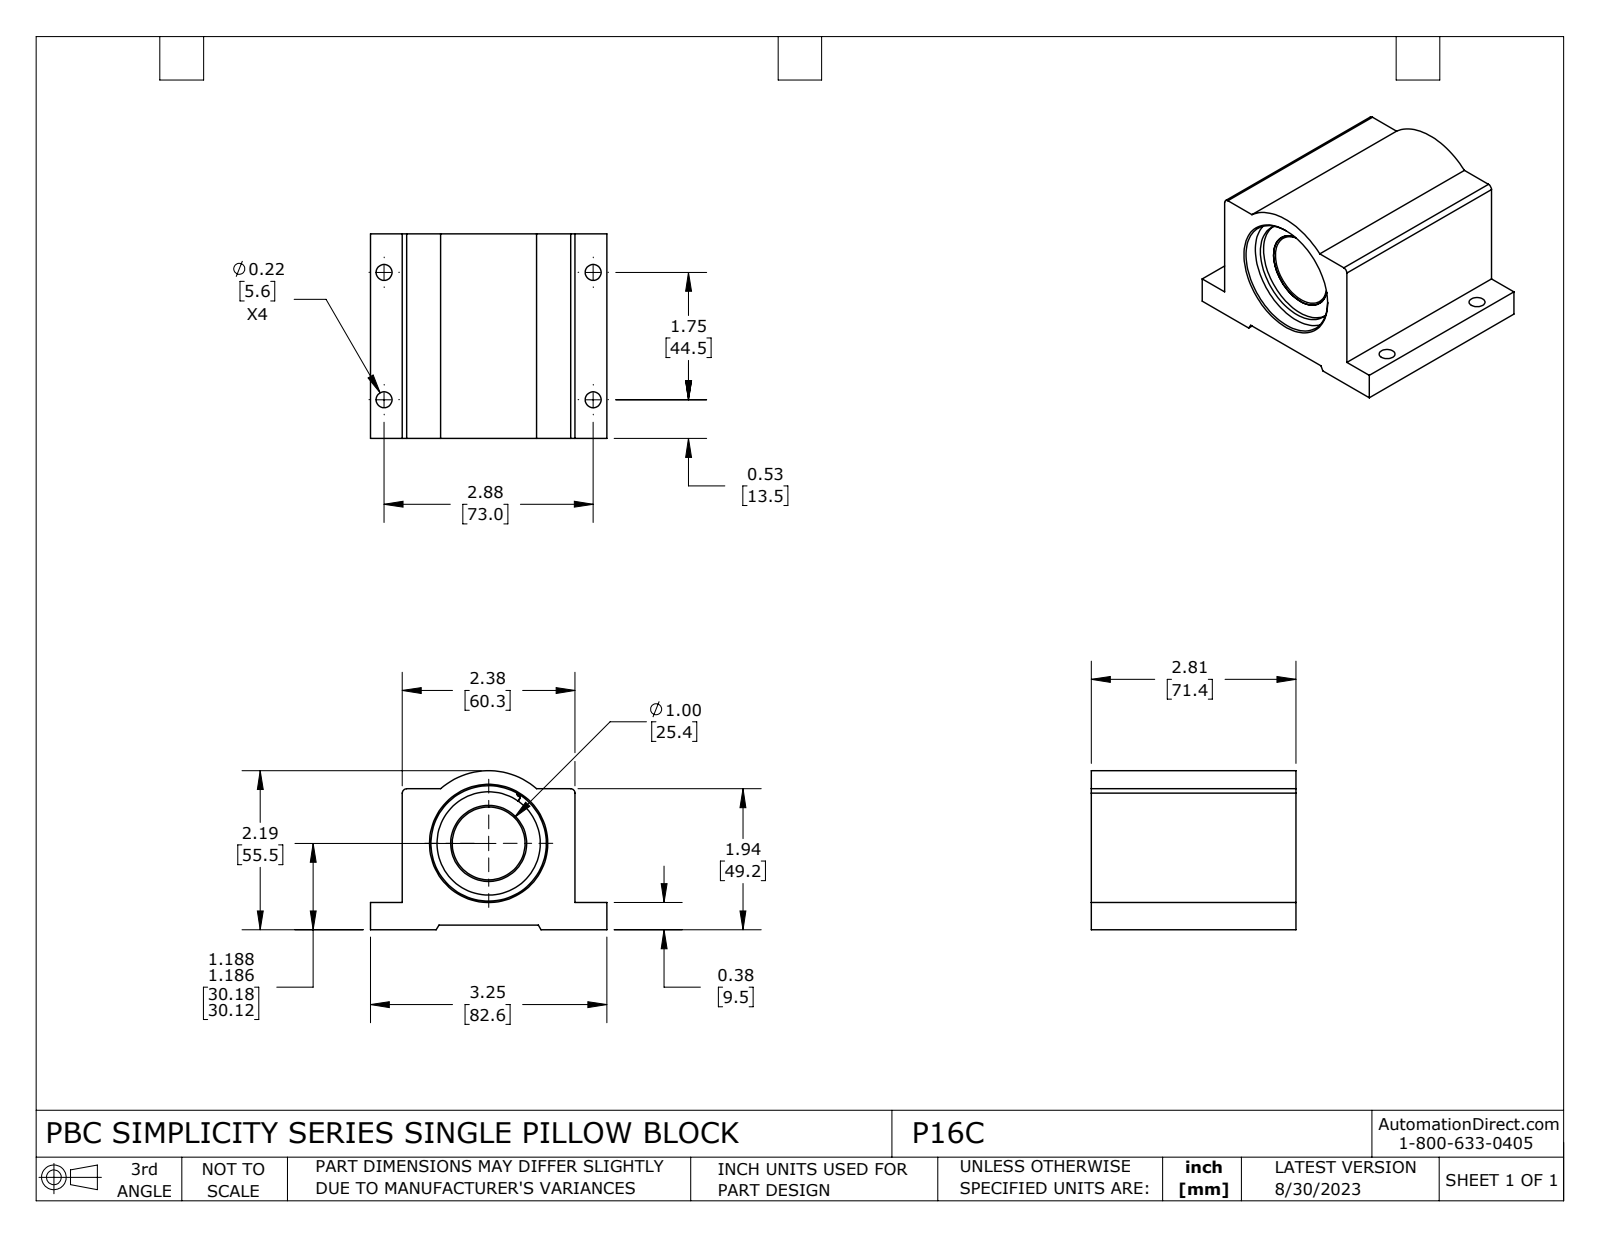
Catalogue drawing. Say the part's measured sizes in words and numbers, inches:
The part is named "P16C". Its 3-D file was written by "SolidWorks 2021 (CONFIG_CONTROL_DESIGN)". It is 7 solids with 164 faces: 45 planar, 71 cylindrical and 48 other. Overall it measures 3.25 by 2.813 by 2.187 inches. Its volume is 11.18 cubic inches and its surface area 94.98 square inches. Round holes: 4 of diameter 0.219, 1 of diameter 1.001, 1 of diameter 1.045, 1 of diameter 1.419, 1 of diameter 1.586, 1 of diameter 1.671. Round bosses or shafts: 1 of diameter 1.675, 1 of diameter 1.562, 1 of diameter 1.471, 1 of diameter 1.399. Partial cylindrical surfaces (rounded edges, fillets, slot ends): 4 of radius 0.021, 2 of radius 0.016, 2 of radius 0.026, 2 of radius 0.06, 1 of radius 1. The main face-to-face distances are 2.375, 0.065, 2.813, 1.938, 1.873, 0.375, 0.31, 1.563, 0.437, 2.812. The hole center spacings are 1.75, 2.875, 3.366.
